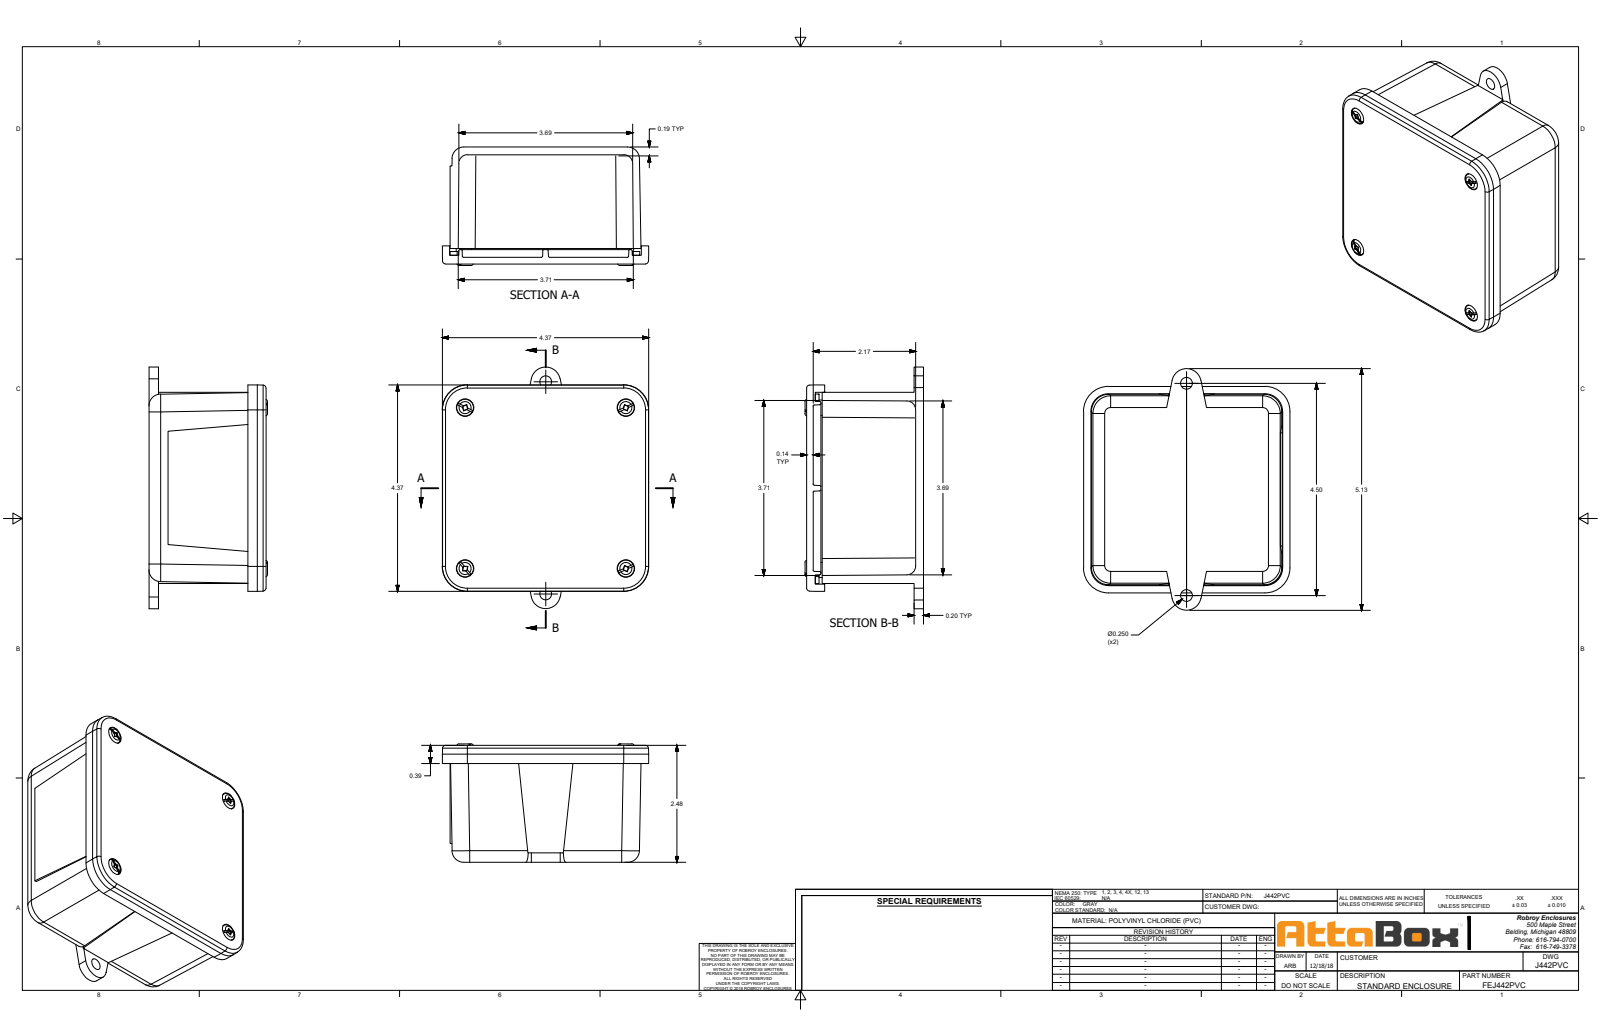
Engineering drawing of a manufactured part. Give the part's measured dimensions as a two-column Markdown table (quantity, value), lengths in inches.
| quantity | value |
| --- | --- |
| part name | J442PVC |
| STEP written by | SolidWorks 2018 (AUTOMOTIVE_DESIGN) |
| units | inches |
| bodies | 15 solids, 585 faces (307 planar, 154 cylindrical, 124 other) |
| overall size | 5.125 × 4.374 × 2.51 |
| volume | 11.99 in³ |
| surface area | 162.2 in² |
| round holes (diameter × count) | 0.25 × 6, 0.13 × 4, 0.187 × 4, 0.19 × 4, 0.2 × 4, 0.223 × 4, 0.335 × 4, 0.37 × 4 |
| round bosses / shafts (diameter × count) | 0.354 × 4, 0.325 × 4, 0.187 × 4, 0.177 × 4 |
| partial cylindrical surfaces (radius × count) | 0.025 × 24, 0.005 × 16, 0.375 × 8, 0.069 × 4, 0.188 × 4, 0.234 × 4, 0.25 × 4, 0.529 × 4 |
| main face-to-face distances | 2.479, 0.165, 2.314, 2.339, 2.174, 0.14, 2.294, 2.129, 0.045, 0.185 |
| hole center spacings | 3.41, 3.42, 3.438, 3.448, 0.028, 0.03, 1.793, 4.313 |
